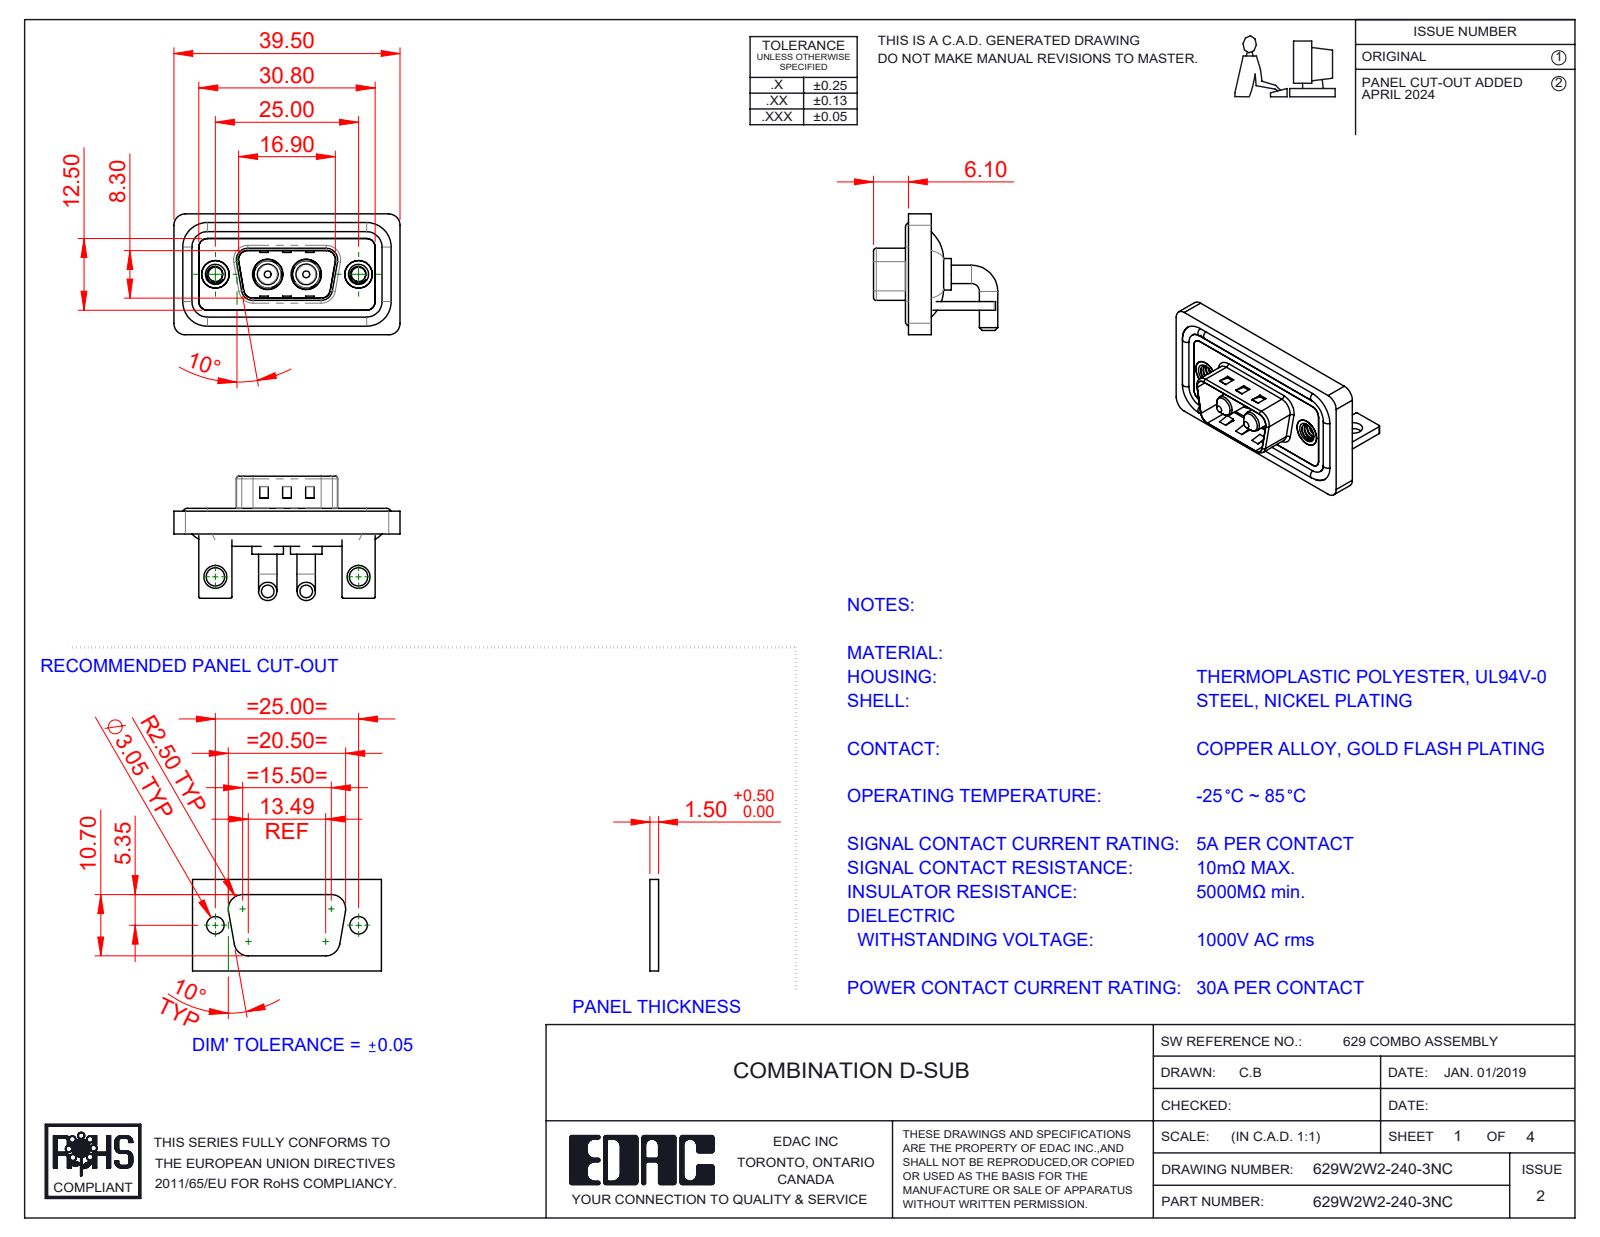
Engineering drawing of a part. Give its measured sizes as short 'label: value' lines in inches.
name: 629W2W2-140-3NC; 629Combo Threaded Rivet_B; 629Combo Shell Front_09 Contacts; 629Combo Housing_2W2 (+4 more)
written by: SolidWorks 2023 (CONFIG_CONTROL_DESIGN)
unit: in
bodies: 13 solids, 535 faces (185 planar, 240 cylindrical, 110 other)
size: 1.555 × 0.854 × 0.831
volume: 0.3 in³; area: 12.08 in²
holes: 2× ⌀0.098, 2× ⌀0.126, 2× ⌀0.157, 2× ⌀0.189, 2× ⌀0.191, 2× ⌀0.197, 2× ⌀0.209
bosses: 4× ⌀0.126, 4× ⌀0.063, 2× ⌀0.217, 2× ⌀0.205, 2× ⌀0.193, 2× ⌀0.187, 2× ⌀0.148, 2× ⌀0.142
rounds: 19× R0.079, 18× R0.059, 16× R0.01, 9× R0.02, 8× R0.063, 4× R0.024, 4× R0.026, 4× R0.035
face distances: 0.016, 0.059, 0.114, 0.031, 0.043, 0.047, 0.083, 0.063, 0.146, 0.098
hole spacings: 0.36, 0.624, 0.984, 0.265
